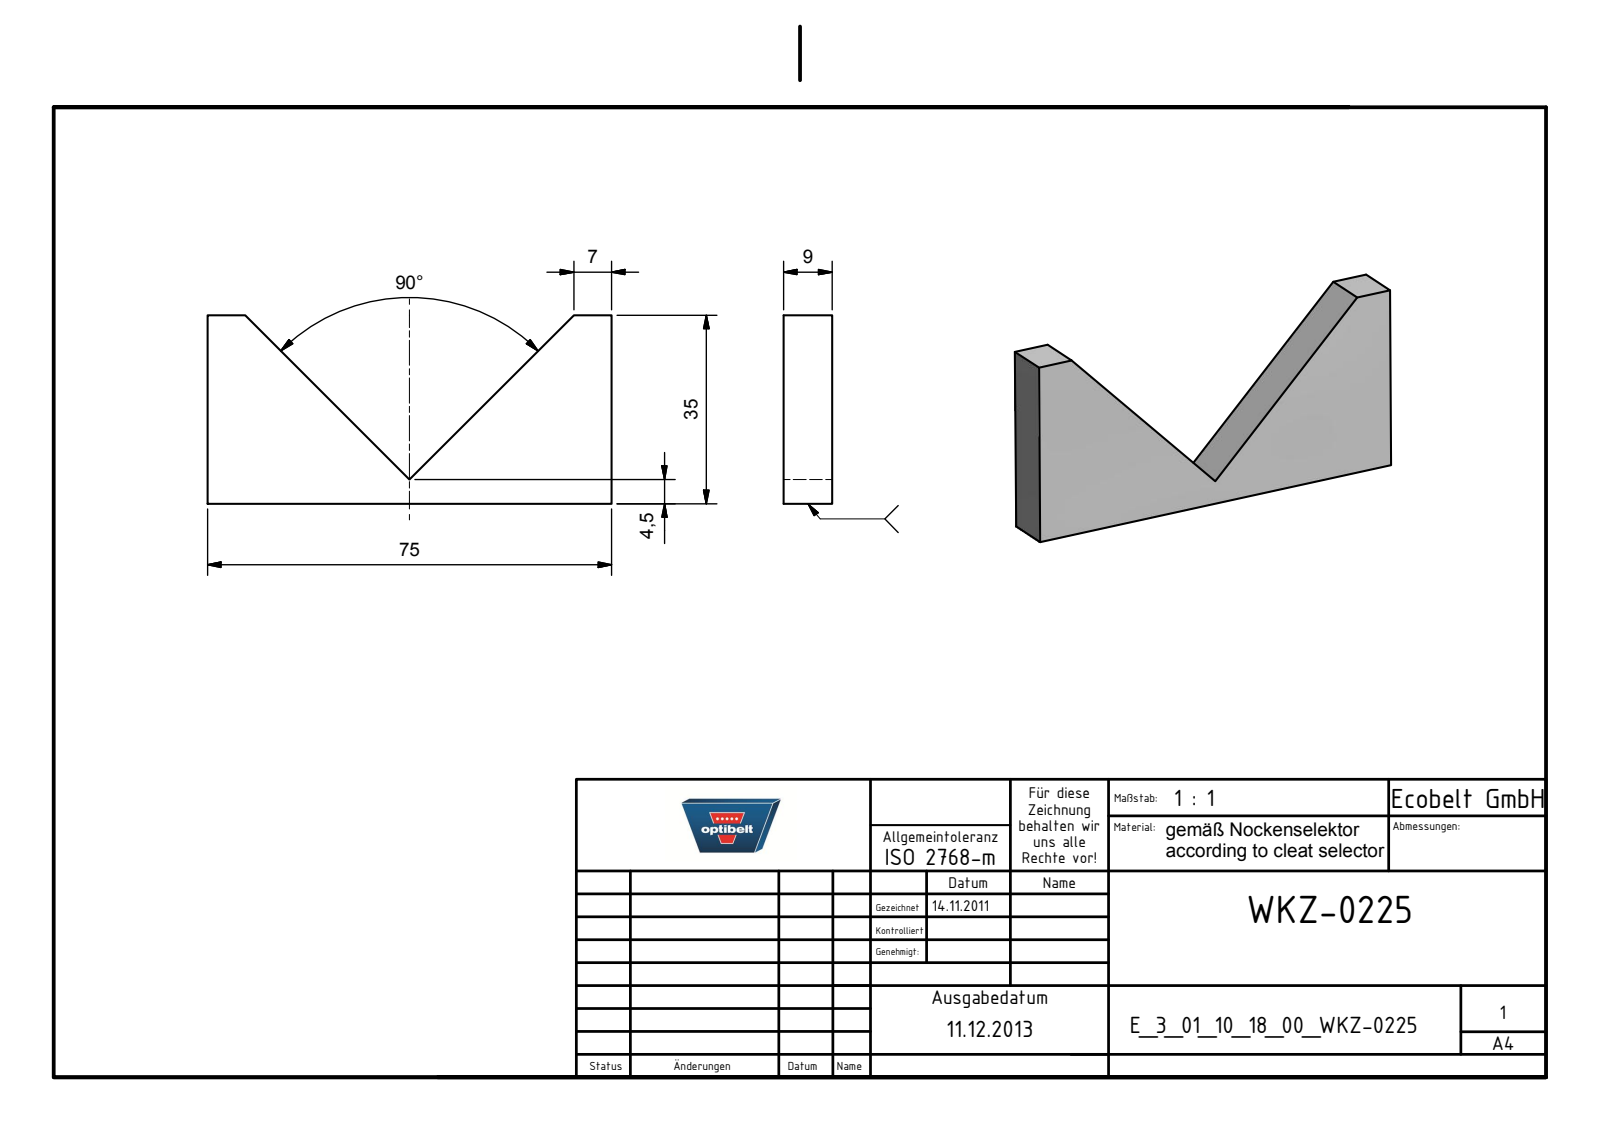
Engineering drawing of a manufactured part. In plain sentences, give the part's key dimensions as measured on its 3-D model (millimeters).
The part is named "E_3_01_10_18_00_WKZ-0225". Its 3-D file was written by "Autodesk Inventor 2025 (AUTOMOTIVE_DESIGN)". It is 1 solid with 9 faces: 9 planar, 0 cylindrical and 0 other. Overall it measures 75 by 35 by 9 millimeters. Its volume is 15 253 cubic millimeters and its surface area 5 597 square millimeters. The main face-to-face distances are 9, 75, 35.
